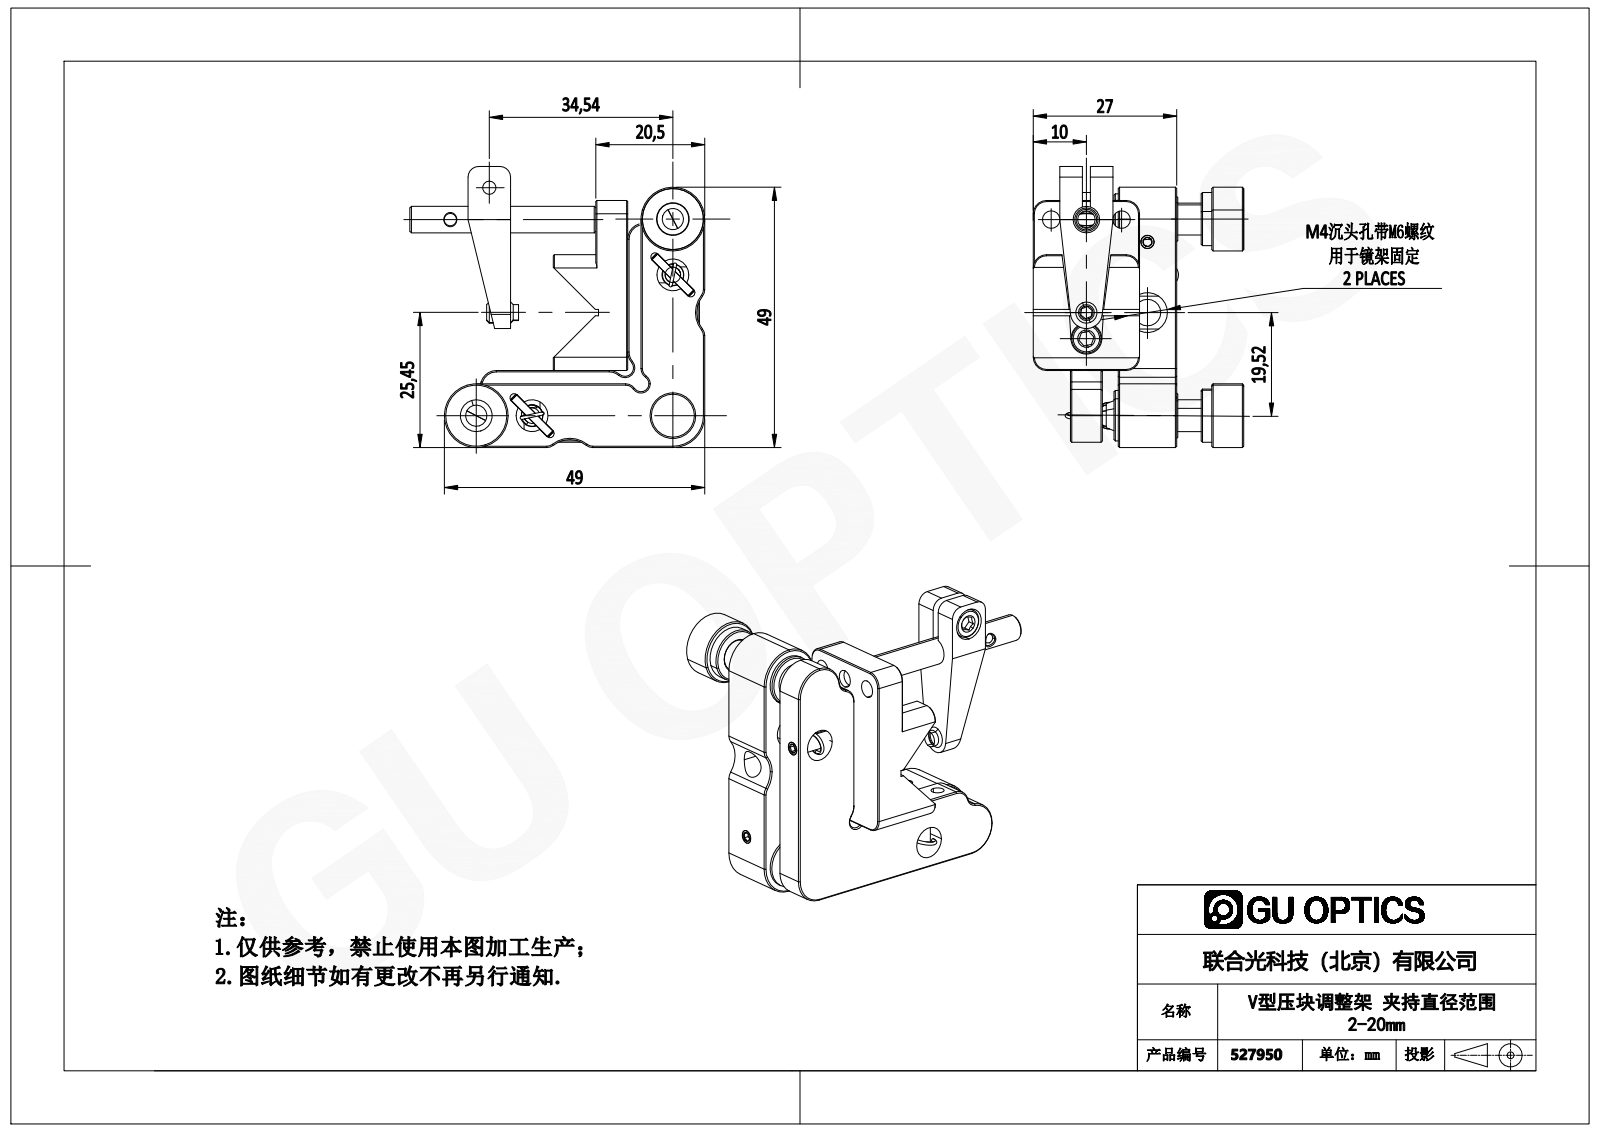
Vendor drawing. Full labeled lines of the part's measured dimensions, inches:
Part name (STEP PRODUCT): 527950
STEP written by: SolidWorks 2020 (CONFIG_CONTROL_DESIGN)
Units: inches
Bodies: 0 solids, 499 faces (177 planar, 148 cylindrical, 174 other)
Overall size (bounding box): 2.185 × 2.083 × 1.559
Round holes (diameter × count): ⌀0.13 ×5, ⌀0.236 ×3, ⌀0.339 ×3, ⌀0.098 ×2, ⌀0.118 ×2, ⌀0.157 ×2, ⌀0.197 ×2, ⌀0.228 ×2, ⌀0.295 ×2, ⌀0.091 ×1
Round bosses / shafts (diameter × count): ⌀0.059 ×4, ⌀0.374 ×3, ⌀0.157 ×3, ⌀0.118 ×3, ⌀0.472 ×2, ⌀0.394 ×2, ⌀0.236 ×2, ⌀0.217 ×2
Partial cylindrical surfaces — rounded edges, fillets, slot ends (radius × count): R0.079 ×10, R0.098 ×6, R0.031 ×4, R0.118 ×3, R0.197 ×3, R0.031 ×2, R0.059 ×1, R0.063 ×1
Main face-to-face distances: 0.433, 0.236, 0.787, 0.551, 0.118, 0.354, 0.276, 0.472, 0.571, 0.098
Hole centre spacings: 0.295, 0.413, 0.481, 0.589, 0.643, 0.737, 0.92, 1.043
